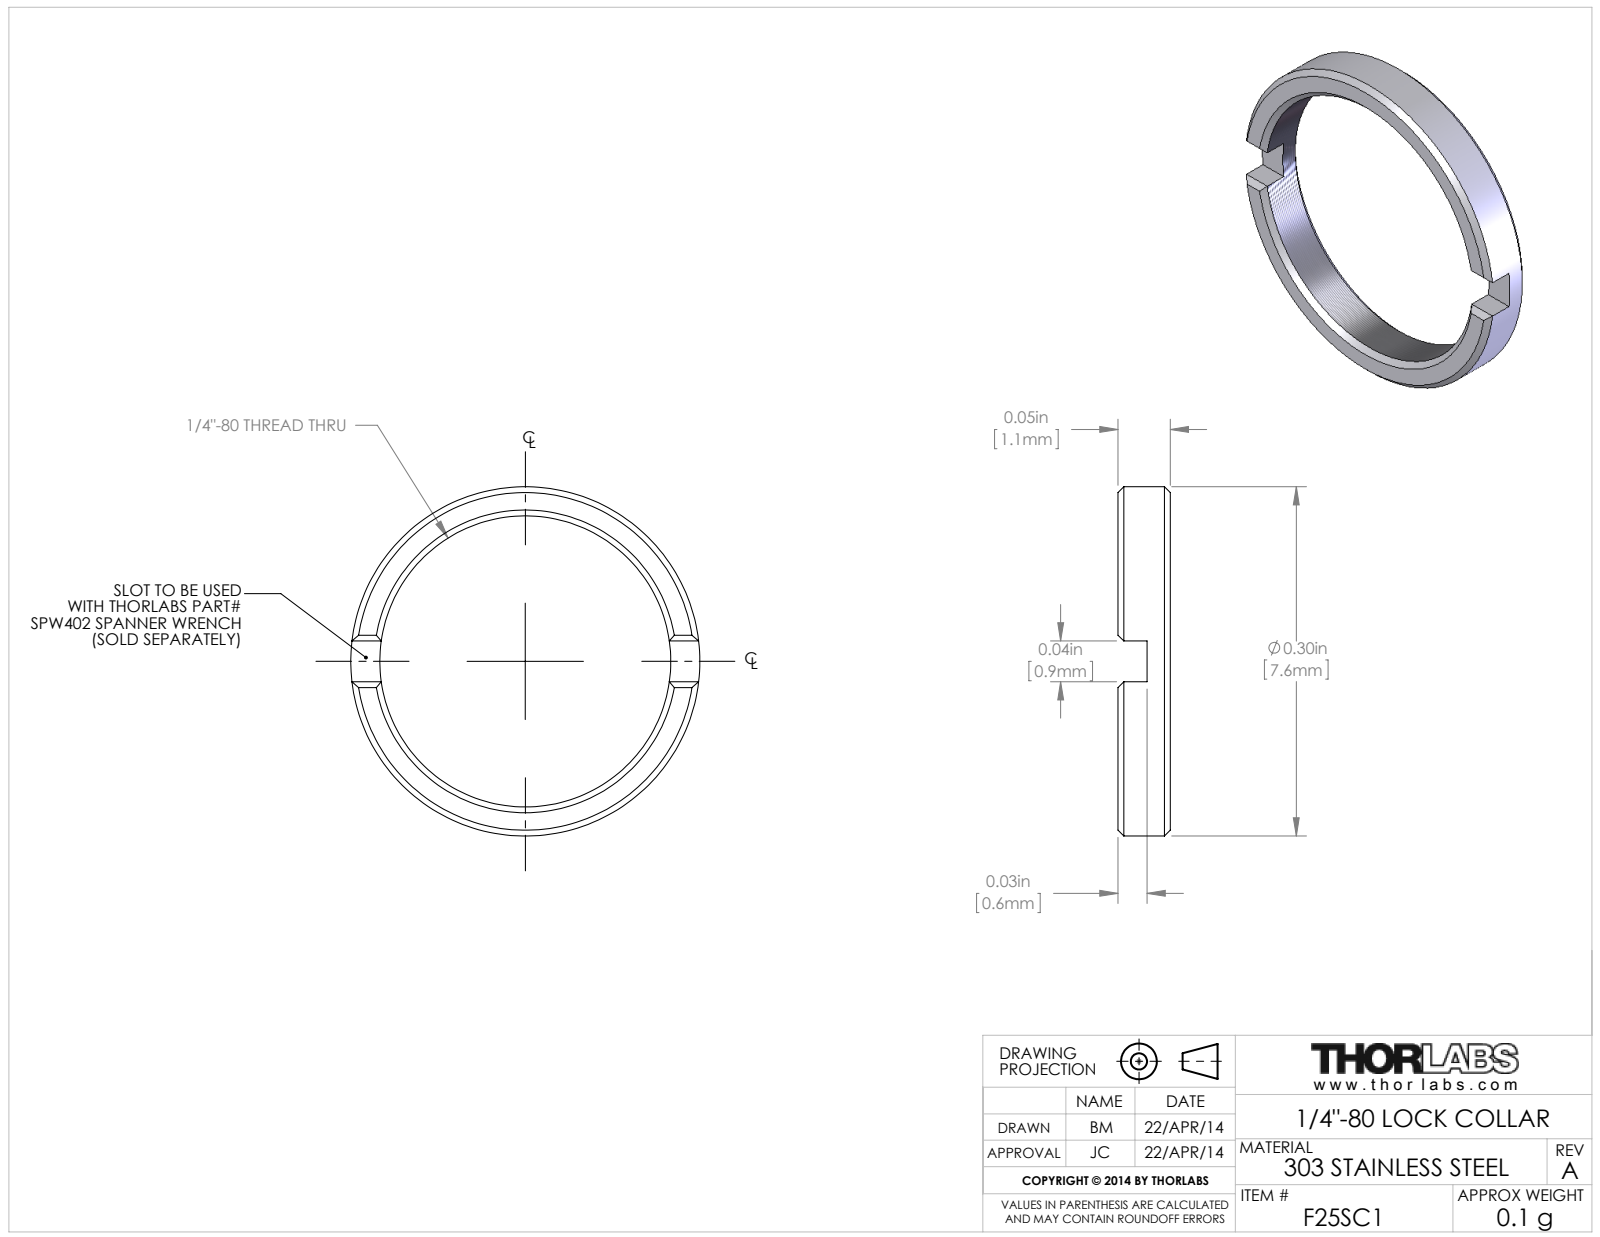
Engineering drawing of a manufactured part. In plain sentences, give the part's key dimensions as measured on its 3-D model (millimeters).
The part is named "TTN024808-E0W". Its 3-D file was written by "SolidWorks 2012 (AUTOMOTIVE_DESIGN)". It is 1 solid with 27 faces: 13 planar, 4 cylindrical and 10 other. Overall it measures 7.62 by 7.62 by 1.14 millimeters. Its volume is 15 cubic millimeters and its surface area 71 square millimeters. Round holes: 1 of diameter 6.35. Round bosses or shafts: 1 of diameter 7.62. The main face-to-face distances are 1.14, 0.51, 0.63, 0.88.
